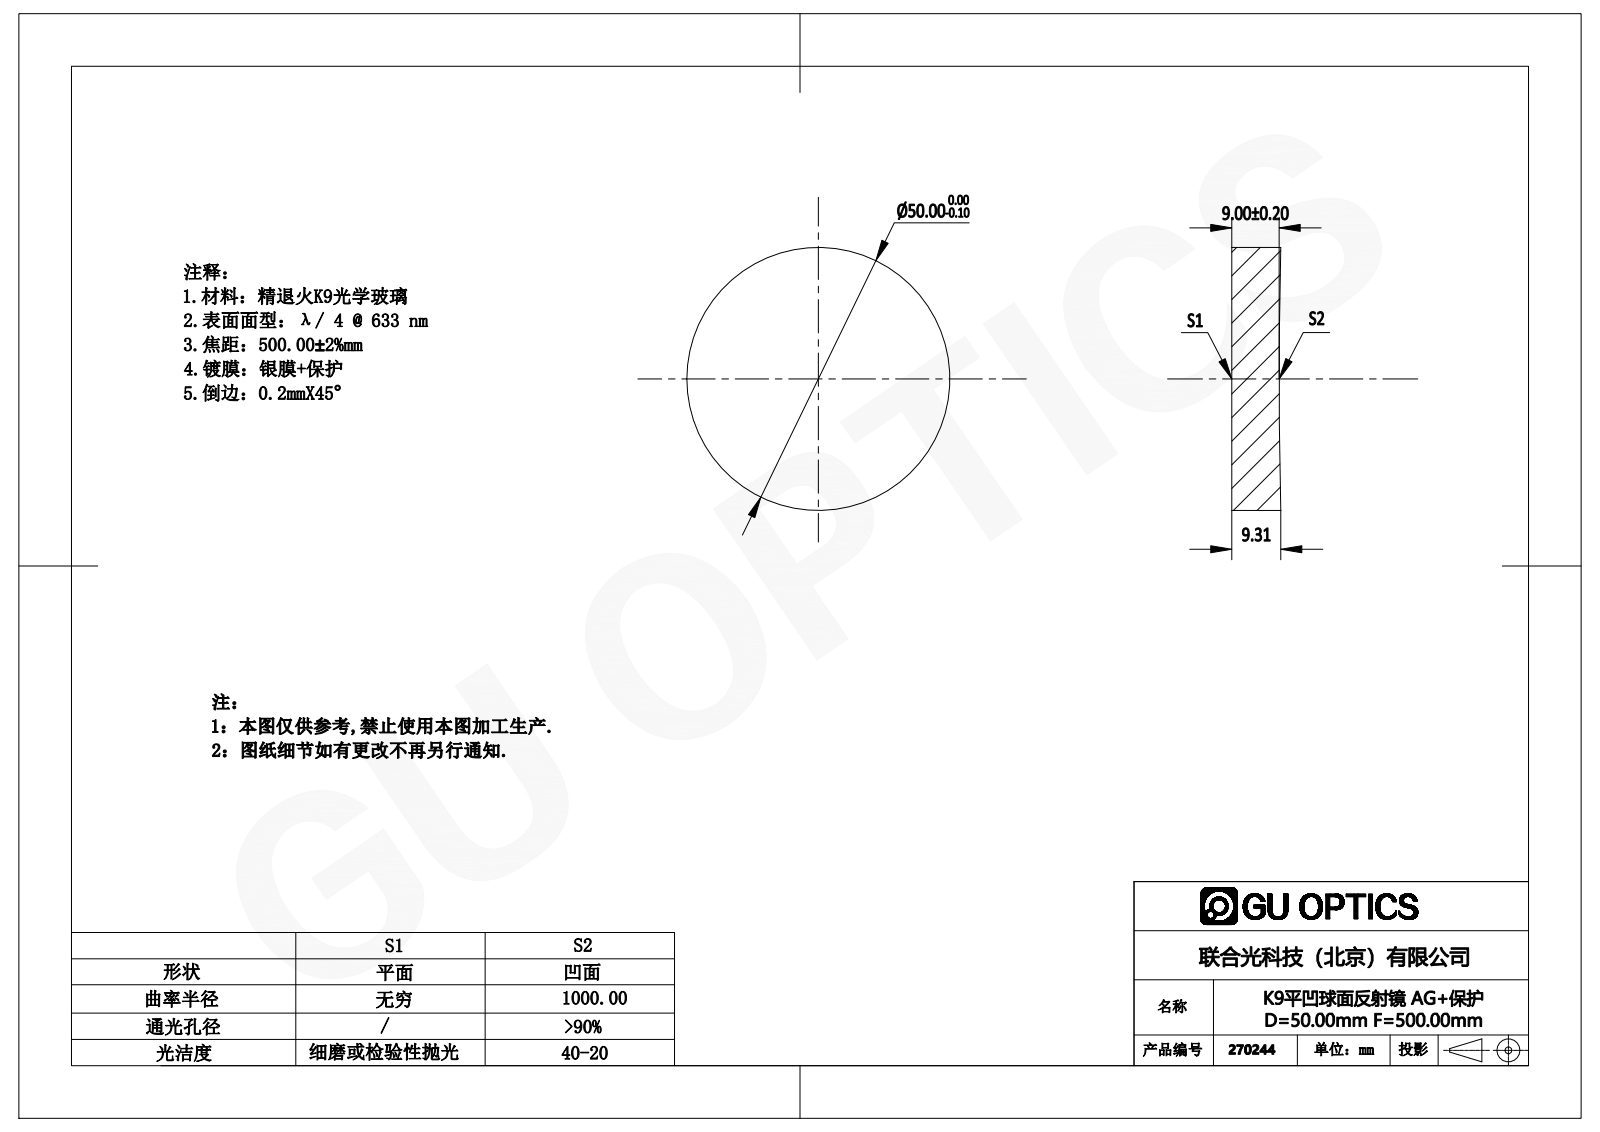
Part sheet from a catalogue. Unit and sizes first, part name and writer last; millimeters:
Units: millimetres
Overall size (bounding box): 50 × 50 × 9.31
Round bosses / shafts (diameter × count): ⌀50 ×1
Volume: 17 978 mm³ · Surface area: 5 390 mm²
Bodies: 1 solid, 5 faces (1 planar, 2 cylindrical, 2 other)
Part name (STEP PRODUCT): 270049
STEP written by: SolidWorks 2016 (AUTOMOTIVE_DESIGN)
